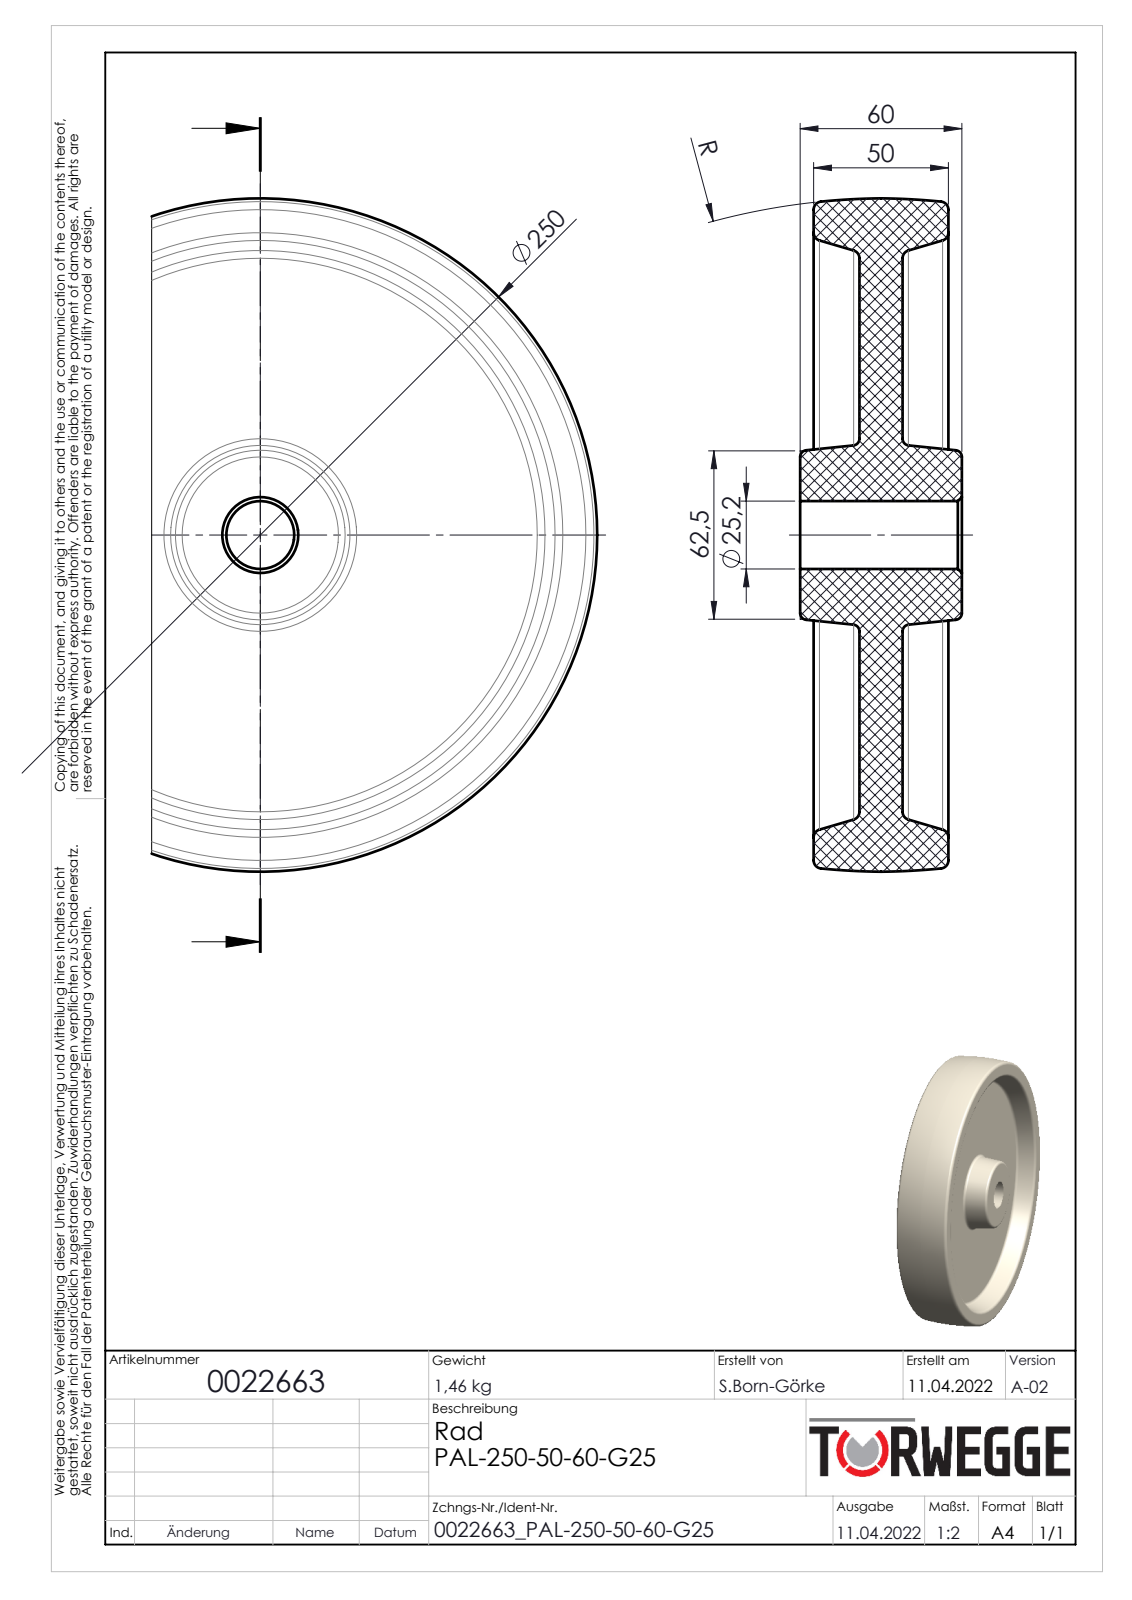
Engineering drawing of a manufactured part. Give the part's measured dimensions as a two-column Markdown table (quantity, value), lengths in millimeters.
| quantity | value |
| --- | --- |
| part name | 0022663 |
| STEP written by | SolidWorks 2020 (AUTOMOTIVE_DESIGN) |
| units | millimeters |
| bodies | 1 solid, 42 faces (6 planar, 2 cylindrical, 34 other) |
| overall size | 250 × 250 × 60 |
| volume | 1 311 000 mm³ |
| surface area | 160 003 mm² |
| round holes (diameter × count) | 25.2 × 1 |
| main face-to-face distances | 16, 17, 33, 50, 5, 22, 38, 55, 60 |
